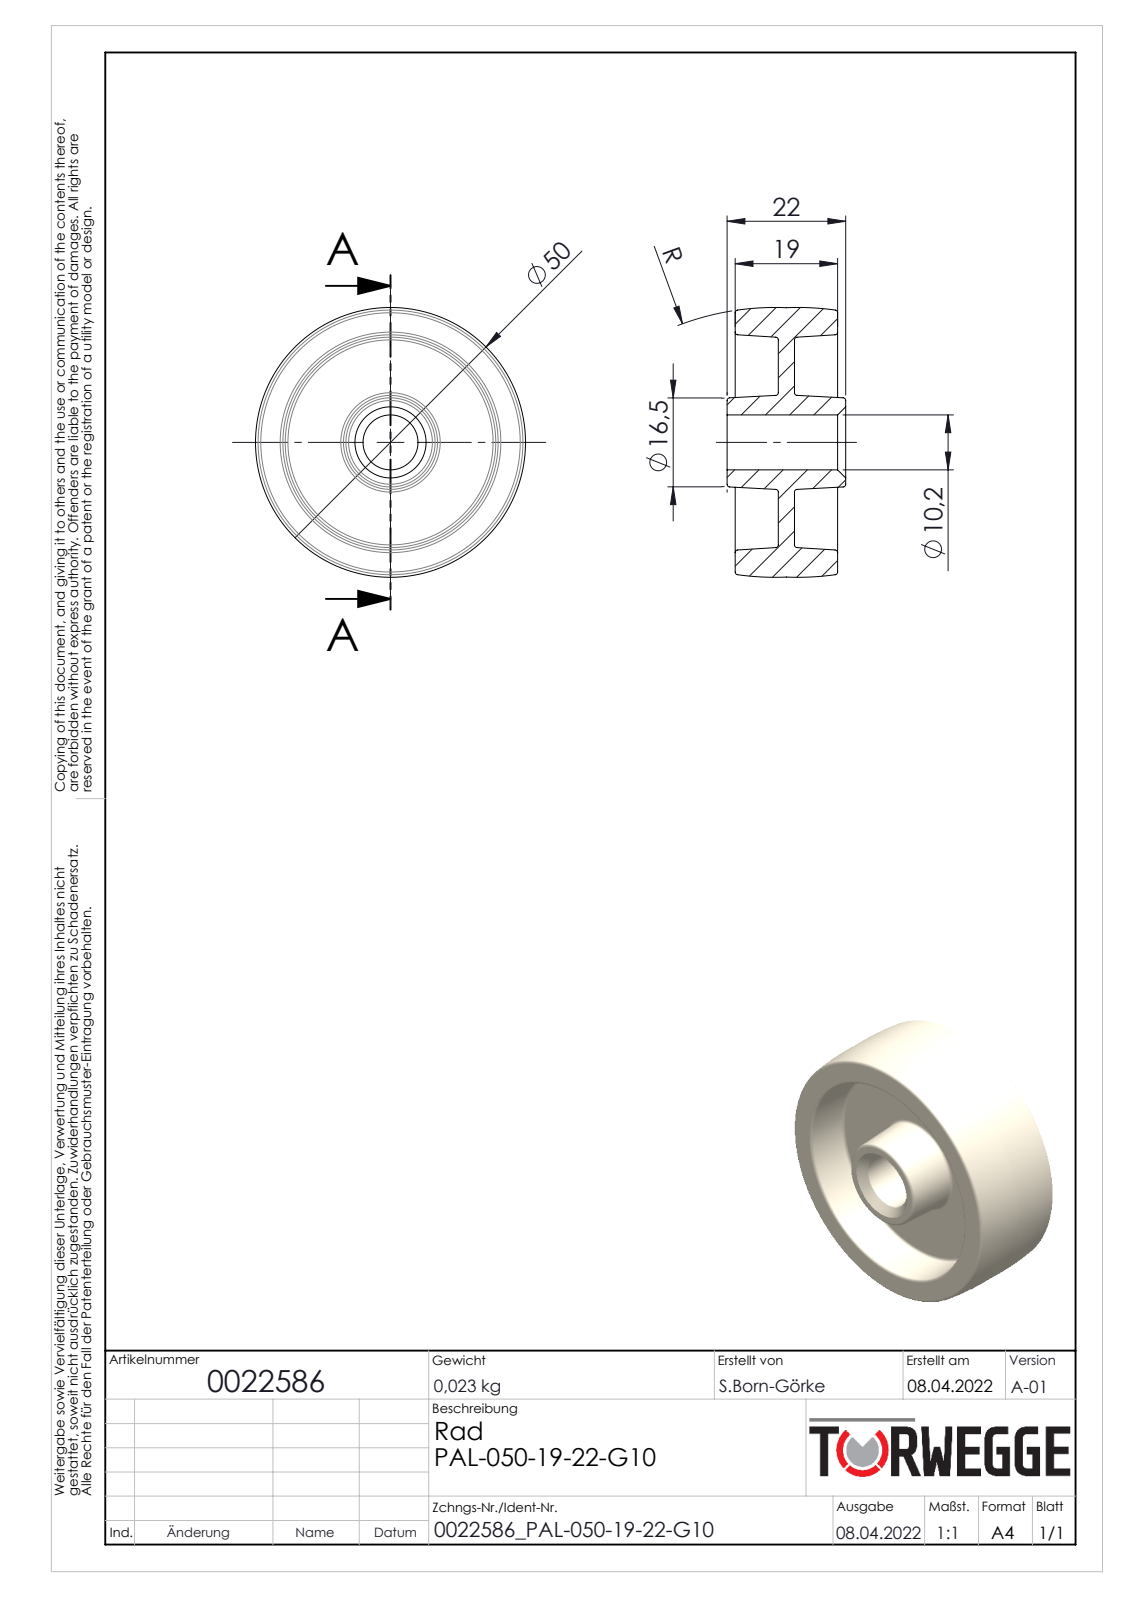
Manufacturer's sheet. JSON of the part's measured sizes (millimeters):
{"part_name": "0022586", "step_written_by": "SolidWorks 2020 (AUTOMOTIVE_DESIGN)", "units": "millimeters", "bodies": {"solids": 1, "faces": 42, "planar": 6, "cylindrical": 2, "other": 34}, "overall_size": [50.09, 50.09, 22], "volume_mm3": 19872, "surface_area_mm2": 9918, "round_holes": [[10.2, 1]], "face_to_face_distances": [8, 11, 3, 19, 1.5, 9.5, 12.5, 20.5, 22]}
